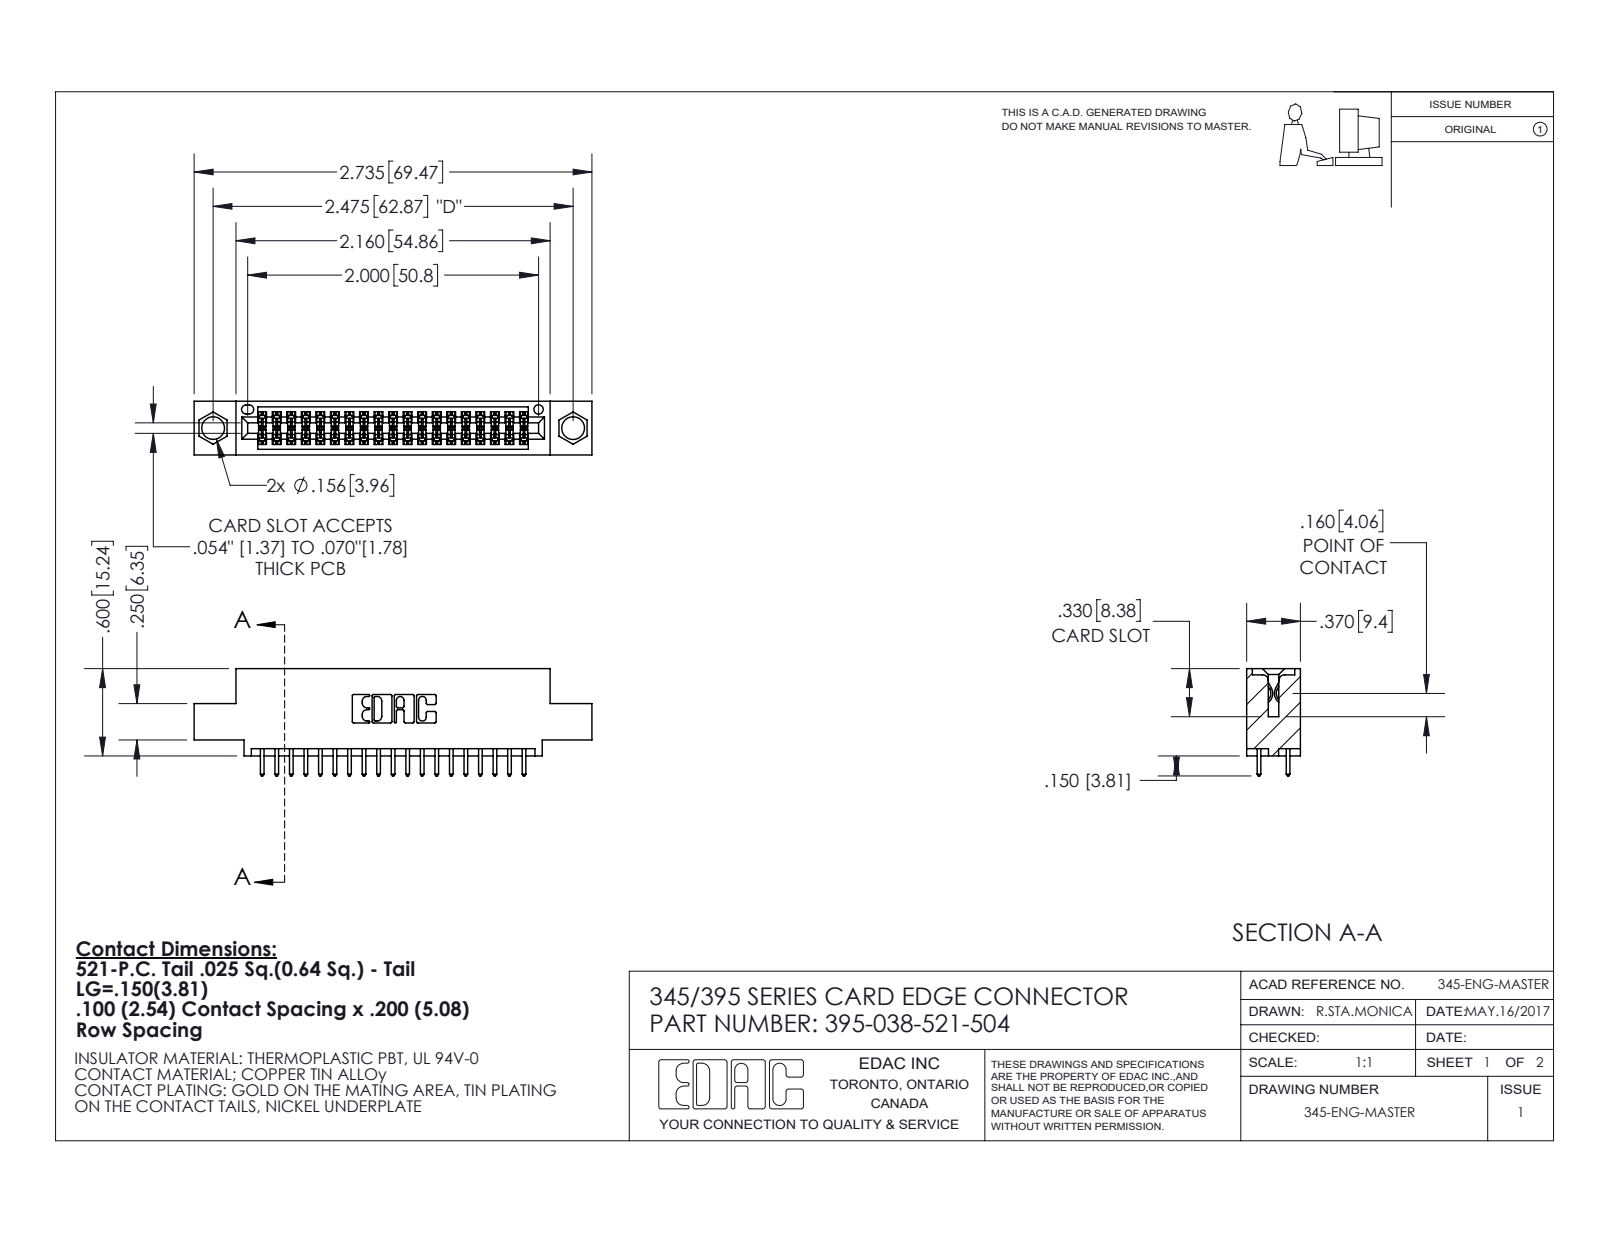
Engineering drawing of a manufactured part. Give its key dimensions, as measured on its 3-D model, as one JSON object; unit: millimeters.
{"part_name": "345-292-001_345-293-121; 395-038-521-504; 345 Part_0.110 Offset - 0.156 Dia-TI", "step_written_by": "SolidWorks 2020 (CONFIG_CONTROL_DESIGN)", "units": "millimeters", "bodies": {"solids": 39, "faces": 2044, "planar": 1352, "cylindrical": 692, "other": 0}, "overall_size": [69.5, 18.7, 9.4], "volume_mm3": 6340, "surface_area_mm2": 8768, "round_holes": [[4, 2], [1.6, 1]], "partial_cylinders_radius": [[0.2, 57], [0.3, 38], [0.3, 22], [0.2, 6], [0.8, 6], [0.7, 3], [0.4, 2], [0.5, 2]], "face_to_face_distances": [1.8, 7.6, 5.1, 9.4, 2.5, 6.9, 0.6, 5.7, 4.4, 3.8], "hole_center_spacings": [6.9, 56.9, 62.9]}
